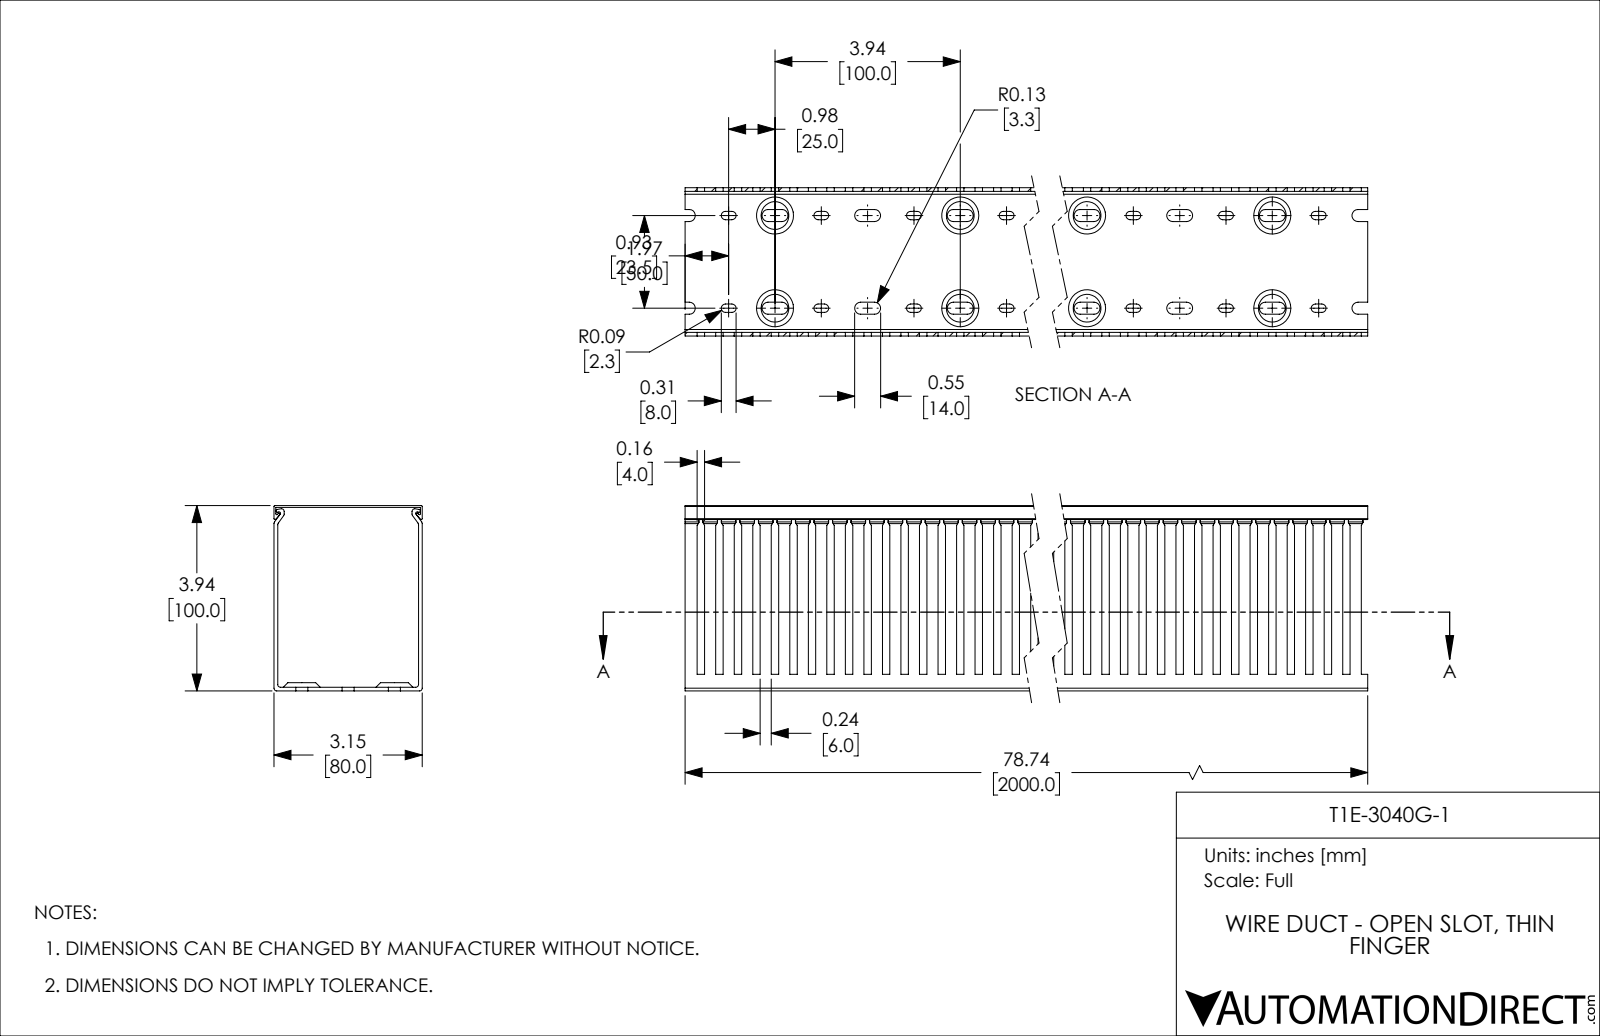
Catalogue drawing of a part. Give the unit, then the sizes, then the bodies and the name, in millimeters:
Units: millimetres
Overall size (bounding box): 2000 × 100 × 80
Partial cylindrical surfaces — rounded edges, fillets, slot ends (radius × count): R3.25 ×200, R2.25 ×160, R1.5 ×12, R0.5 ×8, R0.75 ×6
Main face-to-face distances: 2, 78, 80, 1, 76, 99, 100, 97, 98, 79
Volume: 1 291 000 mm³ · Surface area: 1 492 000 mm²
Bodies: 2 solids, 1573 faces (762 planar, 731 cylindrical, 80 other)
Part name (STEP PRODUCT): T1E-3040W-1
STEP written by: SolidWorks 2021 (CONFIG_CONTROL_DESIGN)
